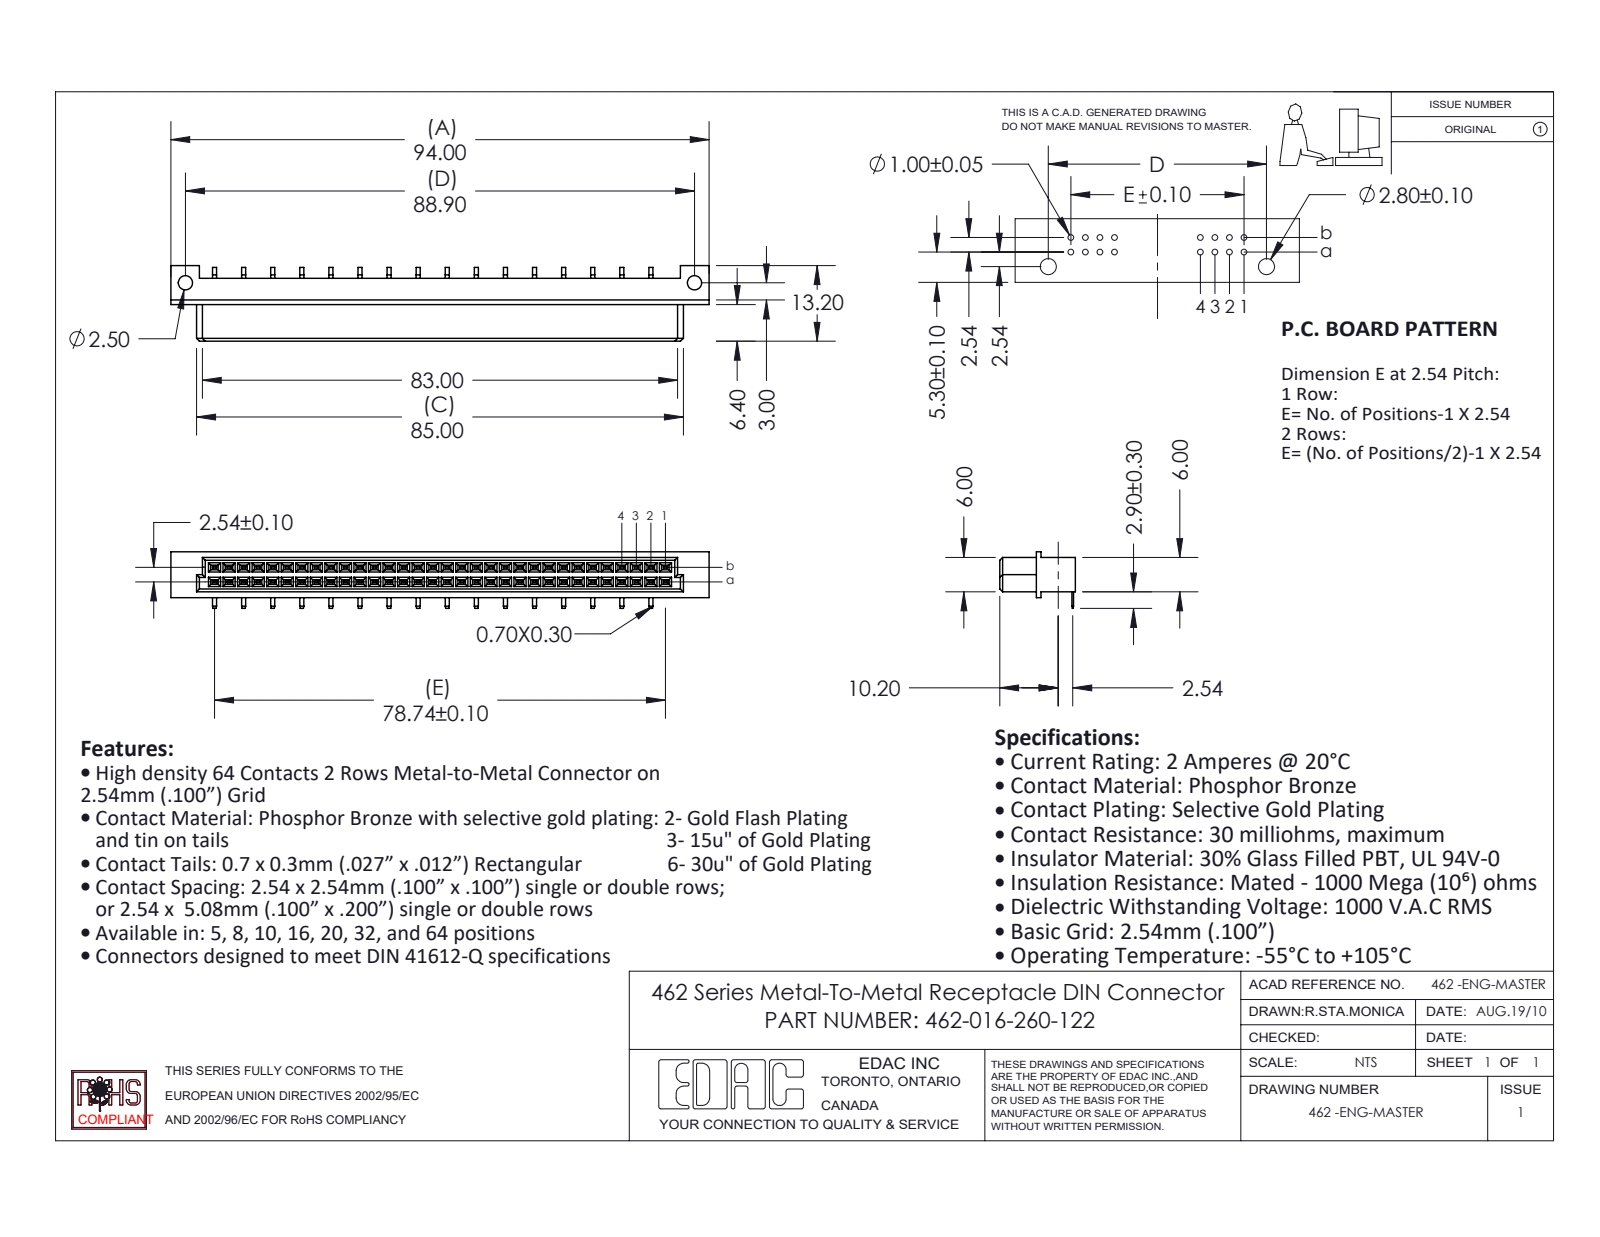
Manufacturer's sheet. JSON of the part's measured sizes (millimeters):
{"part_name": "462-290-1; 462-016-260-122; 462 Part_64", "step_written_by": "SolidWorks 2020 (CONFIG_CONTROL_DESIGN)", "units": "millimeters", "bodies": {"solids": 17, "faces": 1091, "planar": 1055, "cylindrical": 36, "other": 0}, "overall_size": [94, 13.2, 9.9], "volume_mm3": 5527, "surface_area_mm2": 6252, "round_holes": [[2.5, 2]], "partial_cylinders_radius": [[1.02, 1], [1.32, 1]], "face_to_face_distances": [6, 2.54, 0.81, 4.6, 1.32, 2.13, 3.86, 4.67, 3.35, 4.68], "hole_center_spacings": [88.9]}
